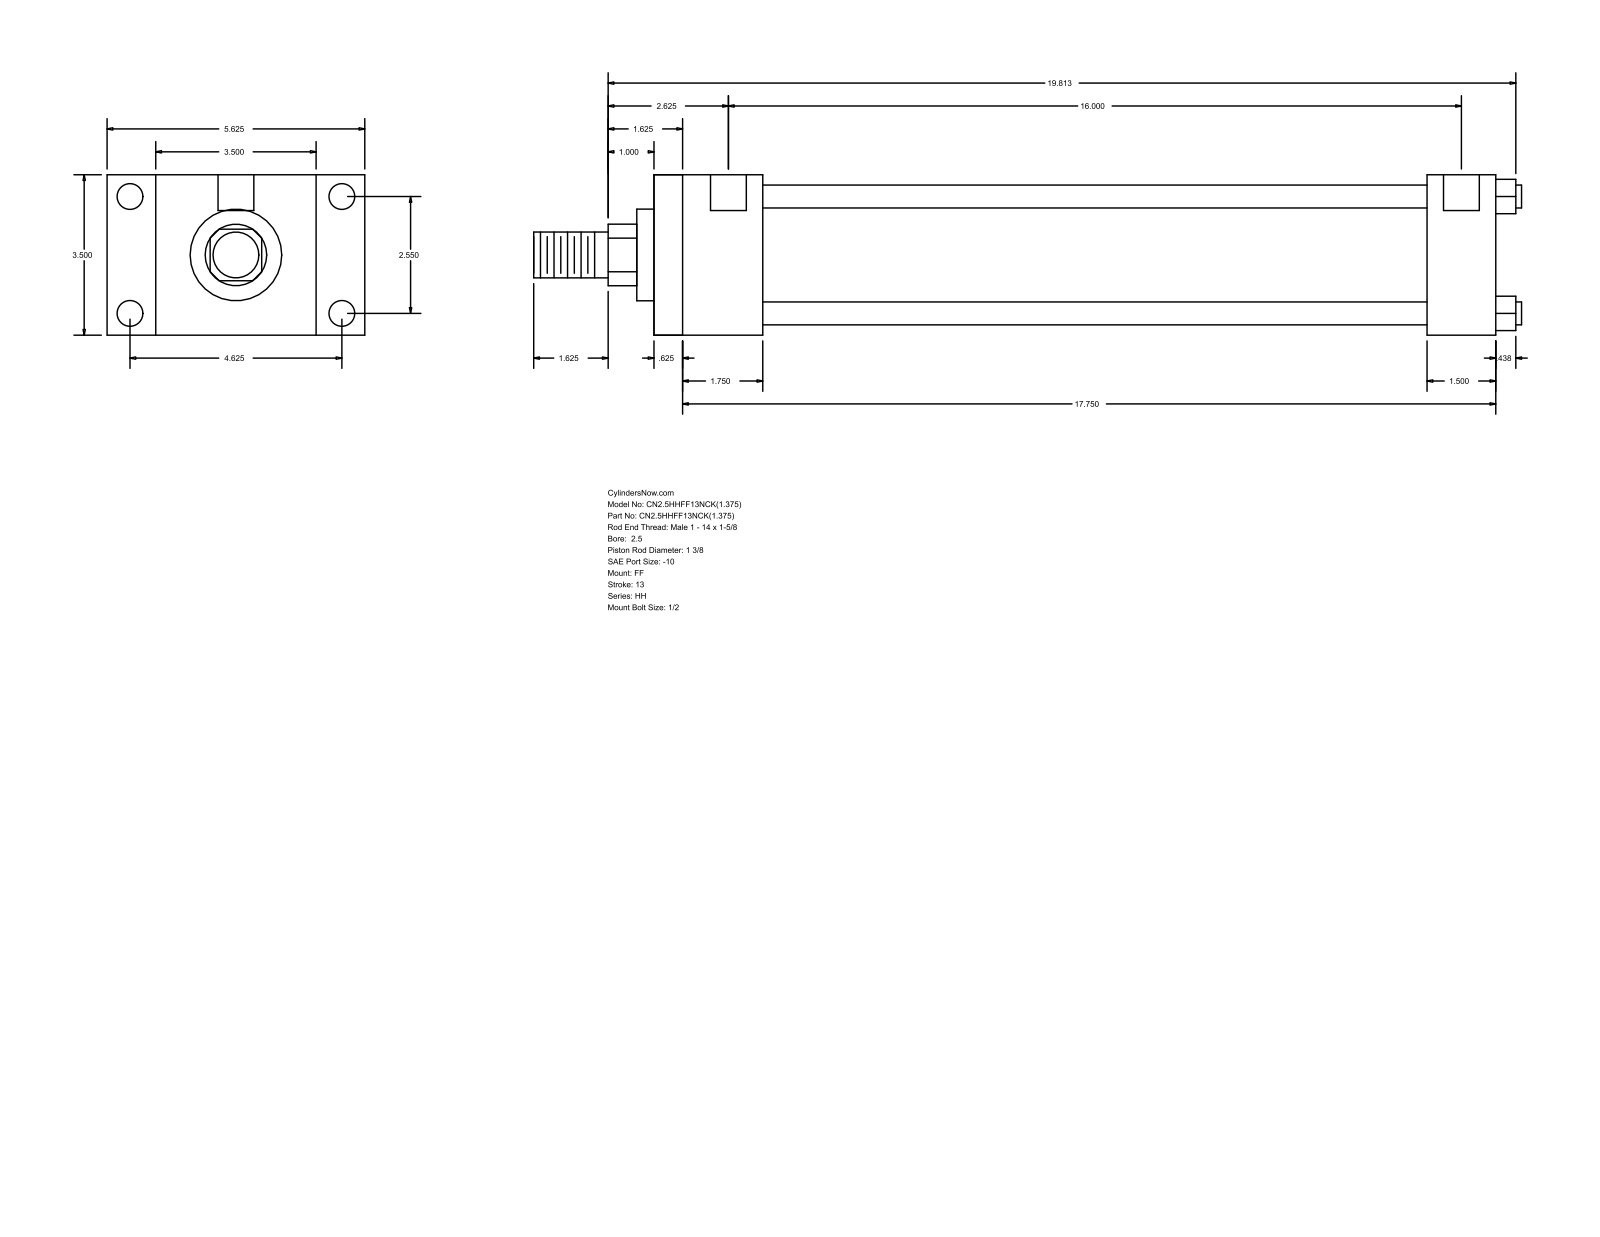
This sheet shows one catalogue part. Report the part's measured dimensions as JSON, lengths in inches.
{"part_name": "HH_FF__0250_1.375", "step_written_by": "GSSL Pune (CONFIG_CONTROL_DESIGN)", "units": "inches", "bodies": {"solids": 0, "faces": 92, "planar": 64, "cylindrical": 28, "other": 0}, "overall_size": [21.563, 5.625, 3.5], "round_holes": [[0.219, 4], [0.563, 4], [0.781, 2]], "round_bosses_or_shafts": [[0.5, 4], [2.875, 1], [2, 1], [1.375, 1], [1, 1]], "partial_cylinders_radius": [[0.672, 1]], "face_to_face_distances": [3.5, 18.375, 0.625, 17.75, 2.375, 1.75, 16, 16.875, 16.25, 14.5], "hole_center_spacings": [2.55, 4.625, 5.281, 16.125, 0.062, 0.063, 16, 16.062]}
